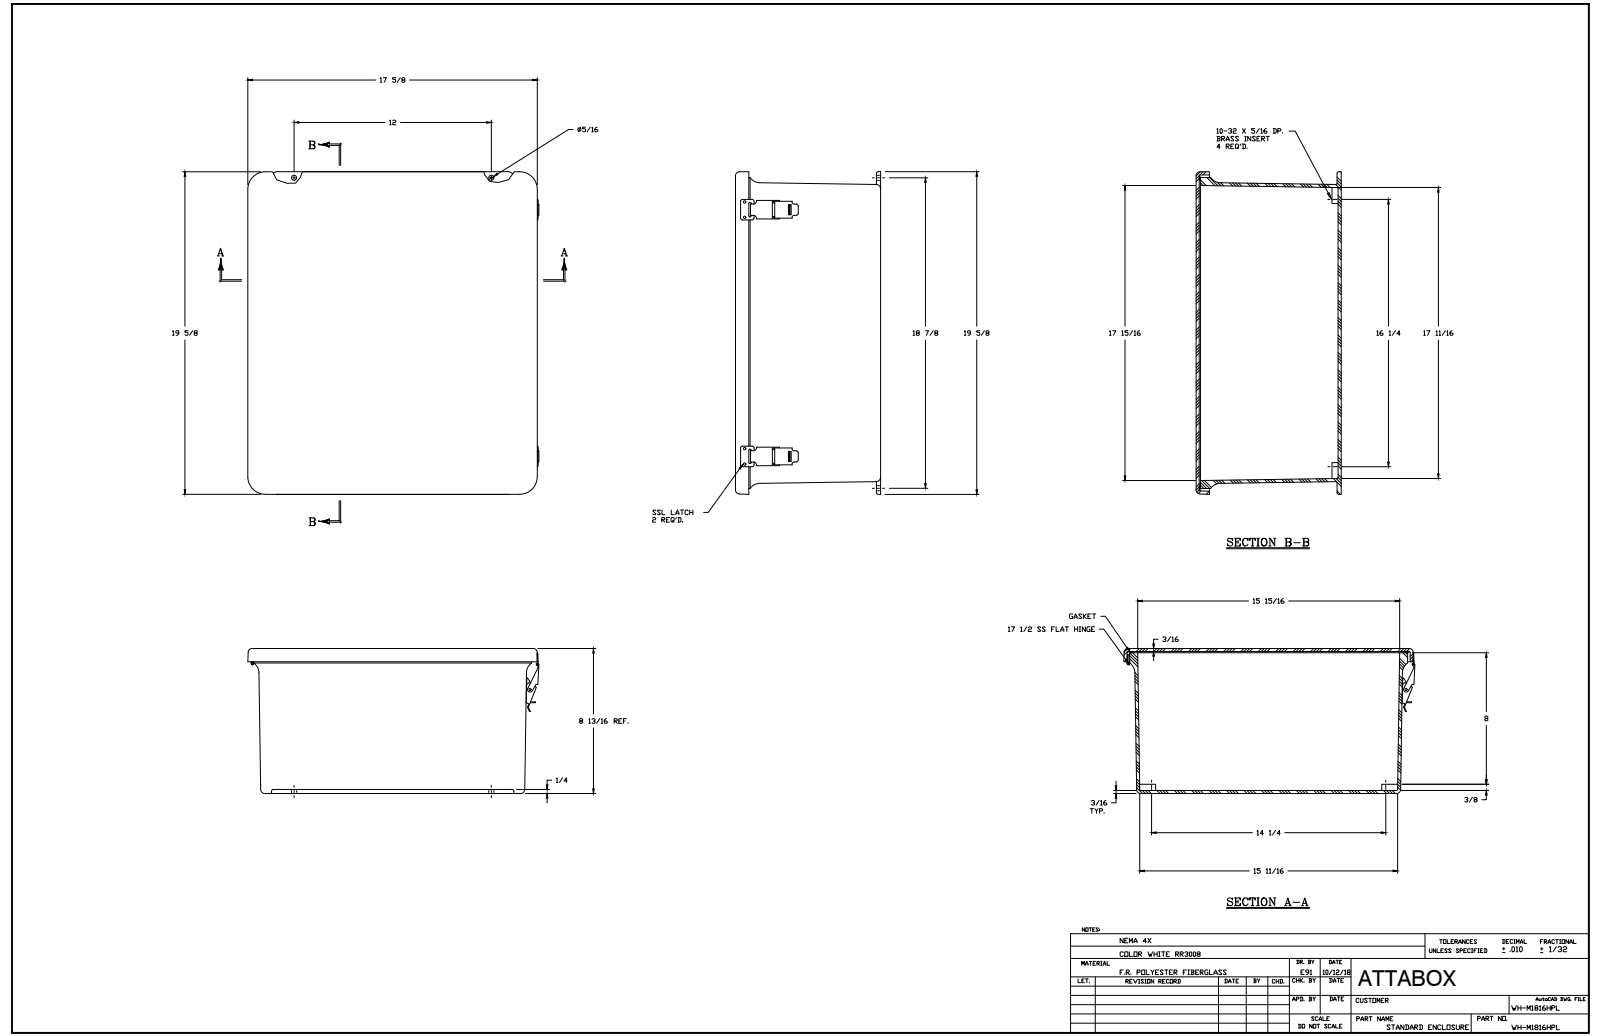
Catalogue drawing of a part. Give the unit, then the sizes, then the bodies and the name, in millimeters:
Units: millimetres
Overall size (bounding box): 498.5 × 449.7 × 224.2
Round holes (diameter × count): ⌀3.6 ×24, ⌀3.3 ×12, ⌀2.6 ×8, ⌀3.9 ×5, ⌀3.3 ×4, ⌀4 ×4, ⌀5.5 ×4, ⌀3.4 ×2, ⌀9.5 ×2, ⌀2.2 ×1, ⌀3.4 ×1
Round bosses / shafts (diameter × count): ⌀6.4 ×12, ⌀3.2 ×11, ⌀3.2 ×9, ⌀6.9 ×4, ⌀7.6 ×1, ⌀4.3 ×1, ⌀3.9 ×1, ⌀3.9 ×1
Partial cylindrical surfaces — rounded edges, fillets, slot ends (radius × count): R0.4 ×20, R0.8 ×20, R3.2 ×20, R1.1 ×16, R0.8 ×12, R0.6 ×8, R6.4 ×8, R1.5 ×6
Main face-to-face distances: 4.7, 219.4, 224.2, 4.8, 214.6, 219.4, 12.4, 7.7, 217.5, 212.7
Hole centre spacings: 85.7, 85.7, 171.5, 6.4, 260.4, 380.6, 247.7, 254
Volume: 4 266 000 mm³ · Surface area: 1 762 000 mm²
Bodies: 42 solids, 1133 faces (509 planar, 473 cylindrical, 151 other)
Part name (STEP PRODUCT): WH-M1816HPL
STEP written by: SolidWorks 2018 (AUTOMOTIVE_DESIGN)
